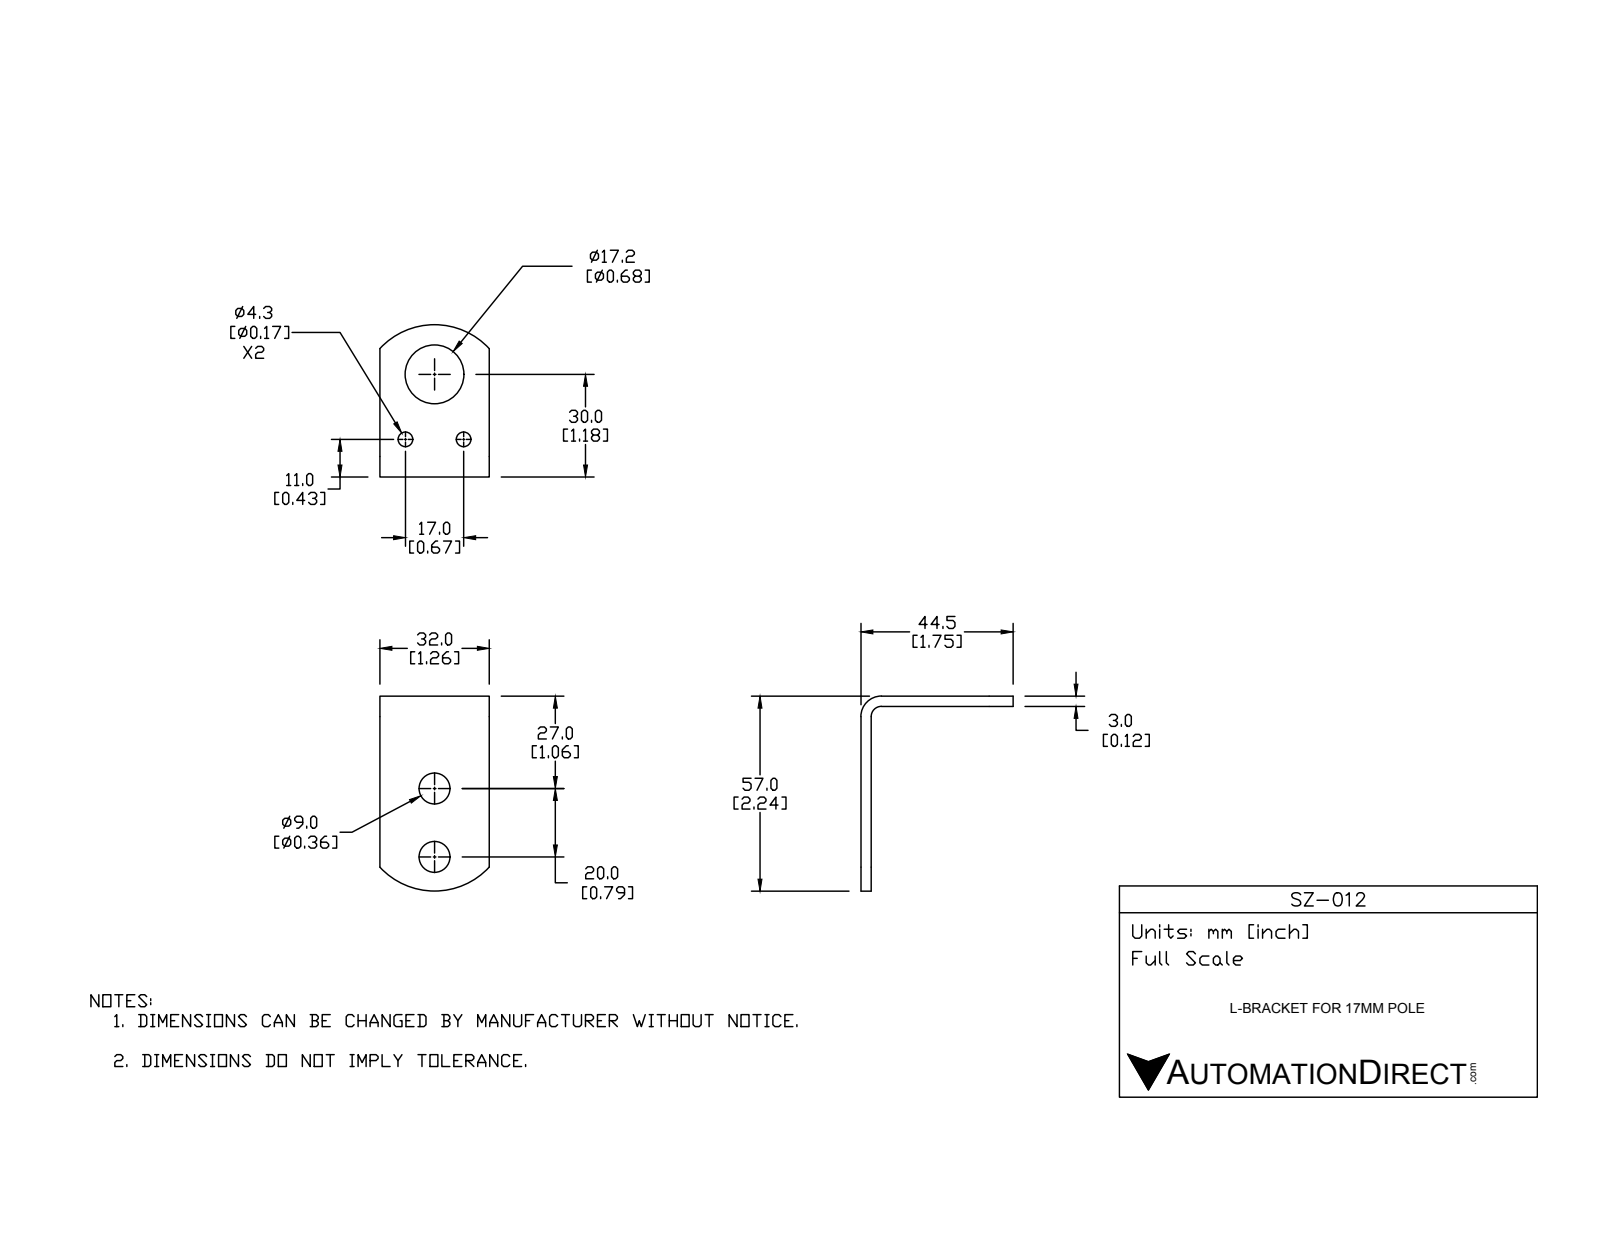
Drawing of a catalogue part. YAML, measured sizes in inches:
part_name: "SZ-012"
step_written_by: "SolidWorks 2016 (AUTOMOTIVE_DESIGN)"
units: inches
bodies: {solids: 1, faces: 24, planar: 10, cylindrical: 14, other: 0}
overall_size: [2.244, 1.772, 1.26]
volume: 0.472
surface_area: 9.74
round_holes:
  - {diameter: 0.169, count: 2}
  - {diameter: 0.356, count: 2}
  - {diameter: 0.677, count: 1}
partial_cylinders:
  - {radius: 0.858, count: 2}
  - {radius: 0.118, count: 1}
  - {radius: 0.236, count: 1}
face_to_face_distances: [0.118, 1.26]
hole_center_spacings: [0.819, 0.669, 0.787]
